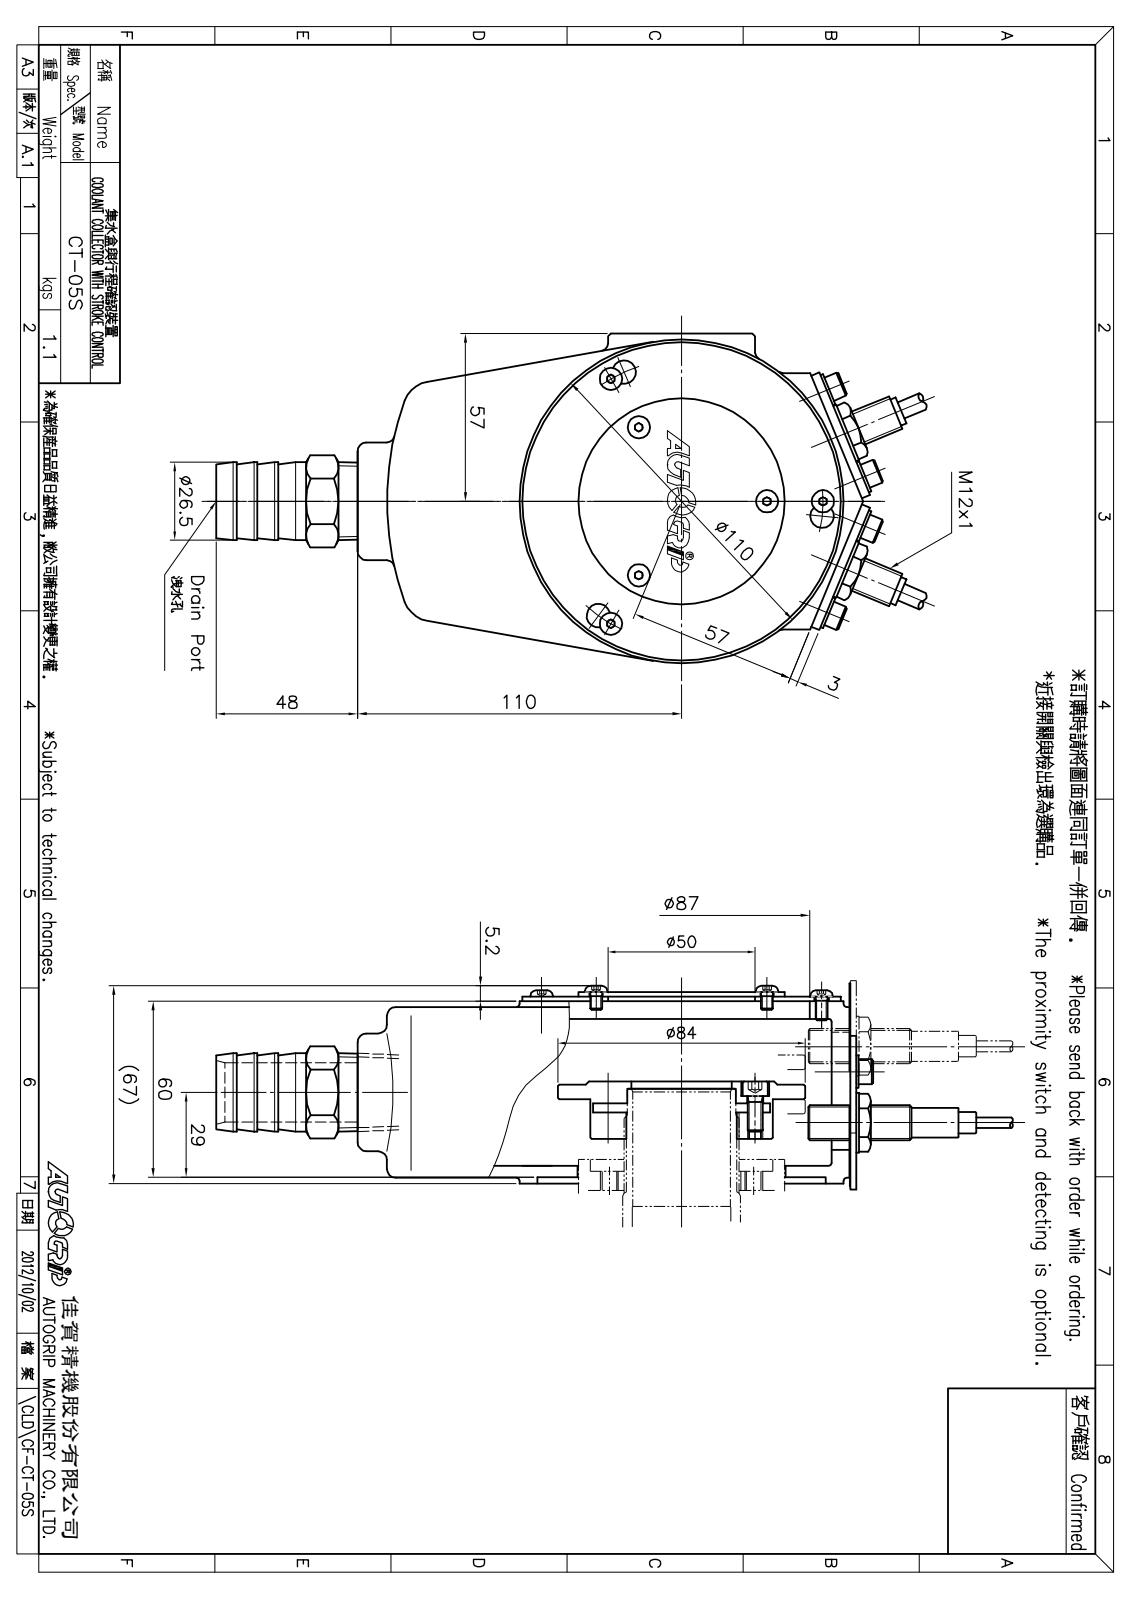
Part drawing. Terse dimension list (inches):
name: CF-CT-05-12000; CT-08洩油管; CF-CT-05-10000; M5x10 (+2 more)
written by: SolidWorks 2016 (CONFIG_CONTROL_DESIGN)
unit: in
bodies: 12 solids, 403 faces (172 planar, 148 cylindrical, 83 other)
size: 9.046 × 4.409 × 2.756
volume: 18.16 in³; area: 240.6 in²
holes: 6× ⌀0.217, 4× ⌀0.197, 3× ⌀0.13, 2× ⌀0.165, 2× ⌀0.394, 2× ⌀0.472, 1× ⌀0.984, 1× ⌀1.339, 1× ⌀1.535, 1× ⌀2.362, 1× ⌀2.776, 1× ⌀3.425
bosses: 4× ⌀0.335, 4× ⌀0.197, 1× ⌀4.331, 1× ⌀4.291, 1× ⌀3.307, 1× ⌀2.441, 1× ⌀1.575, 1× ⌀1.299
rounds: 16× R0.108, 10× R0.118, 8× R0.276, 6× R0.079, 5× R0.098, 3× R0.157, 2× R0.236, 2× R0.394
face distances: 0.157, 0.236, 2.205, 0.079, 1.22, 0.984, 0.059, 2.362, 1.142, 2.126
hole spacings: 1.168, 1.633, 2.31, 2.431, 1.89, 3.273, 0.525, 0.62
